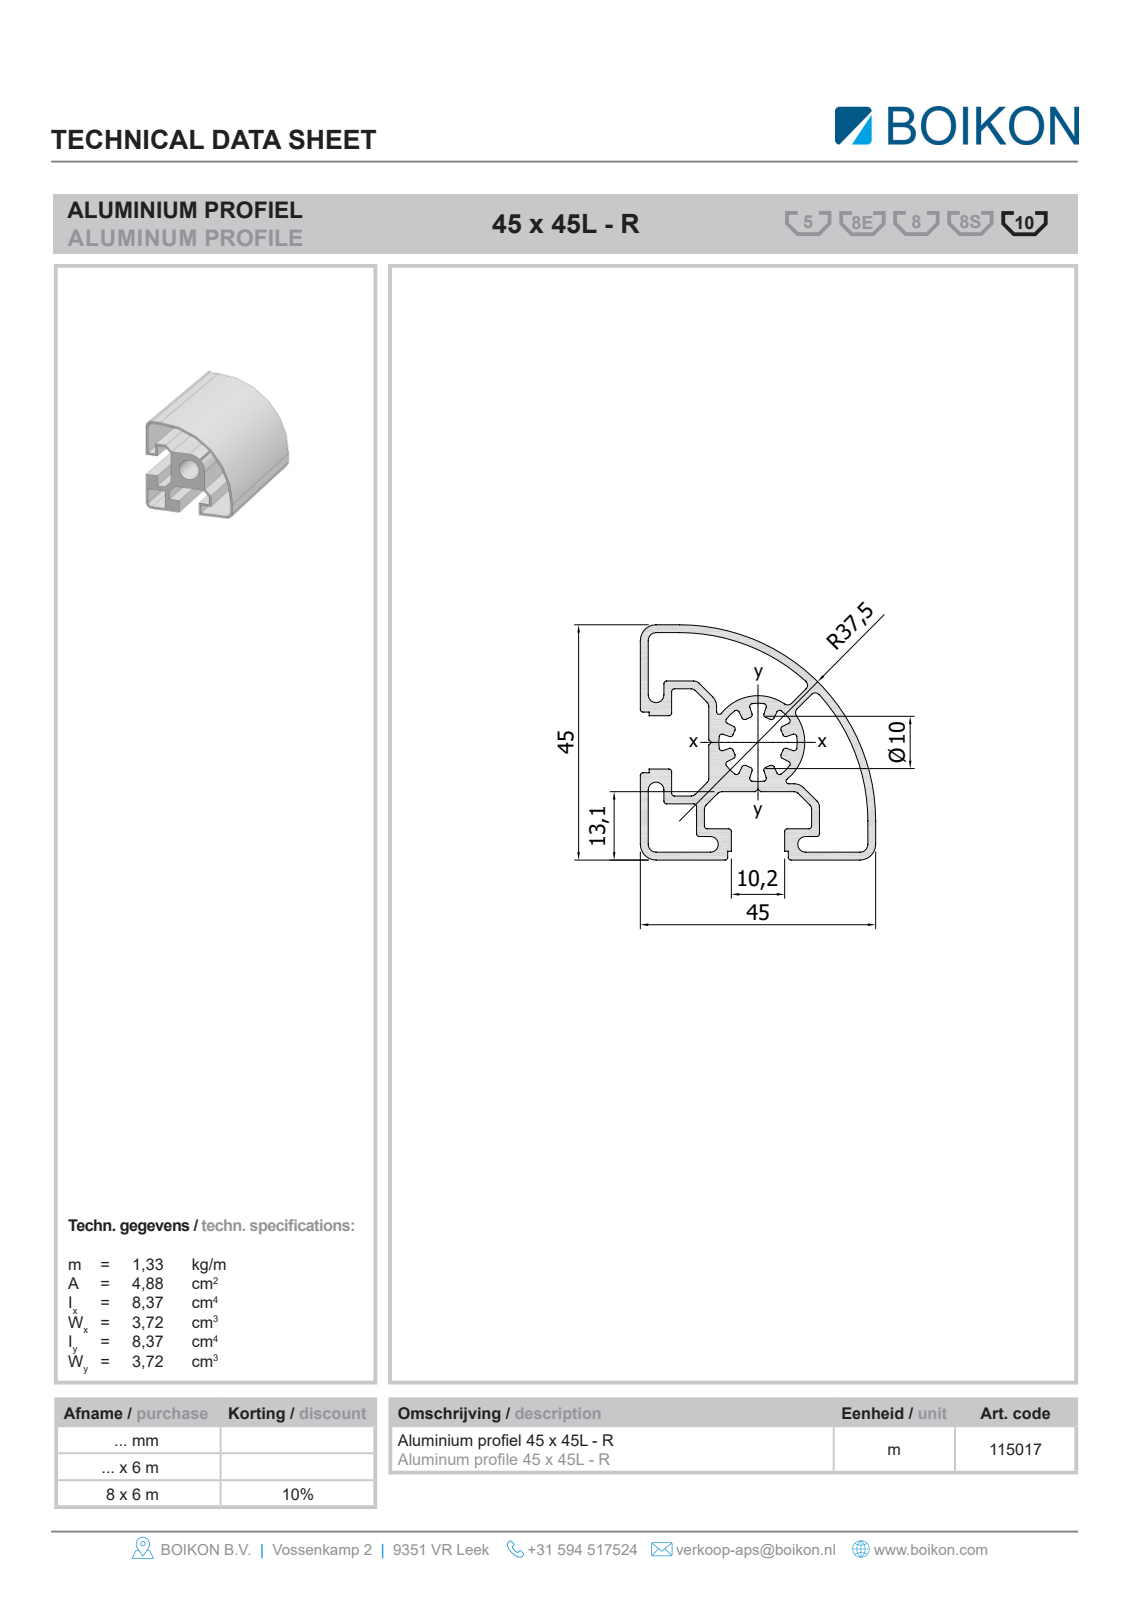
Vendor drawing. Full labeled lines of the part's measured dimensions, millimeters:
Part name (STEP PRODUCT): Root; 11501745x45L-RBOIKON0
STEP written by: HiCAD 2013 1802.4 Build 509 (AUTOMOTIVE_DESIGN)
Units: millimetres
Bodies: 1 solid, 58 faces (46 planar, 12 cylindrical, 0 other)
Overall size (bounding box): 1000 × 45 × 45
Volume: 501 868 mm³ · Surface area: 494 324 mm²
Round holes (diameter × count): ⌀10 ×1
Partial cylindrical surfaces — rounded edges, fillets, slot ends (radius × count): R2 ×3, R3 ×3, R8.15 ×1, R36.5 ×1, R37.5 ×1
Main face-to-face distances: 1, 5, 16.4, 27.6, 3.1, 20.65, 13.1, 12.1, 4, 32.75
